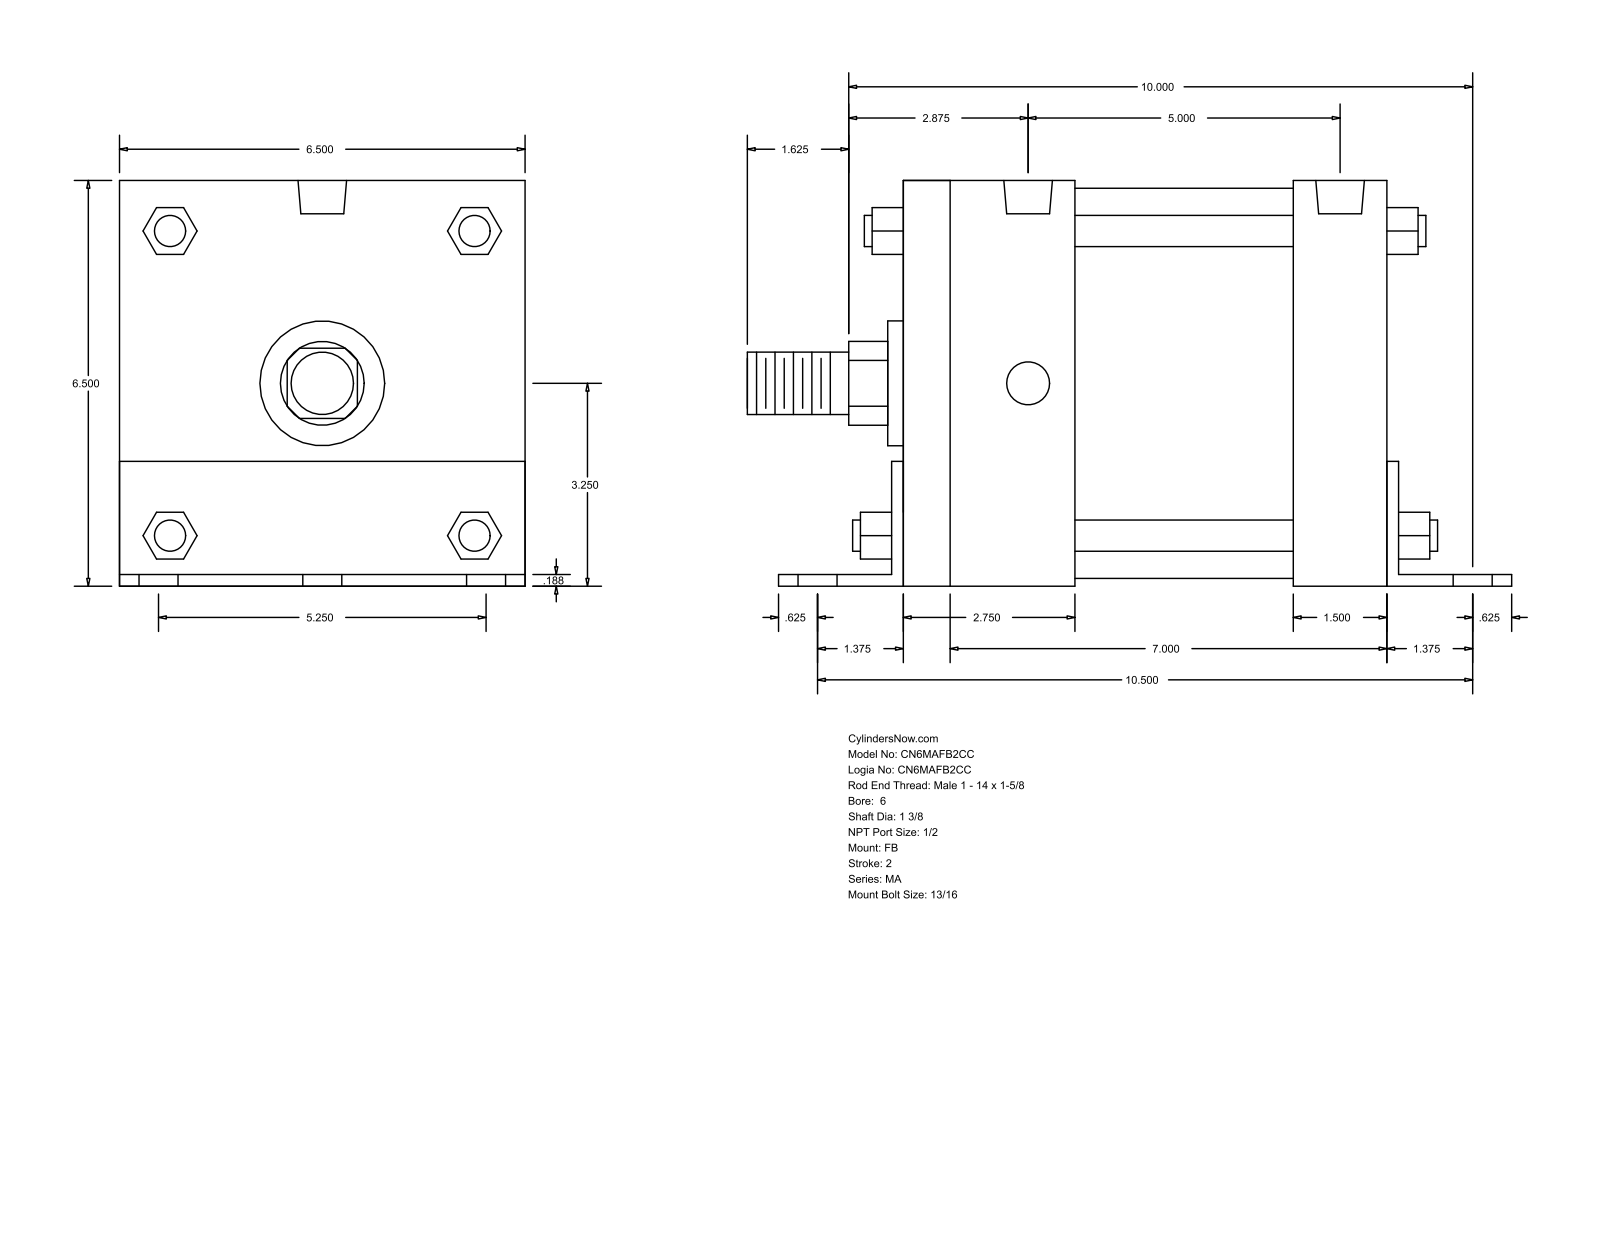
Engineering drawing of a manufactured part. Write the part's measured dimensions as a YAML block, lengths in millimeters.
part_name: "MA_FB__0600_1.375"
step_written_by: "GSSL Pune (CONFIG_CONTROL_DESIGN)"
units: millimeters
bodies: {solids: 0, faces: 140, planar: 105, cylindrical: 35, other: 0}
overall_size: [307.98, 165.15, 165.1]
round_holes:
  - {diameter: 20.64, count: 6}
  - {diameter: 17.46, count: 4}
  - {diameter: 19.77, count: 2}
round_bosses_or_shafts:
  - {diameter: 12.7, count: 4}
  - {diameter: 158.75, count: 1}
  - {diameter: 50.8, count: 1}
  - {diameter: 34.92, count: 1}
  - {diameter: 25.4, count: 1}
partial_cylinders:
  - {radius: 17.06, count: 1}
  - {radius: 32.05, count: 1}
face_to_face_distances: [165.1, 4.76, 193.67, 165.15, 4.71, 160.39, 4.77, 38.1, 42.86, 203.2]
hole_center_spacings: [66.67, 271.82, 263.52, 83.81, 85.78, 108.6, 123.82, 133.34]
